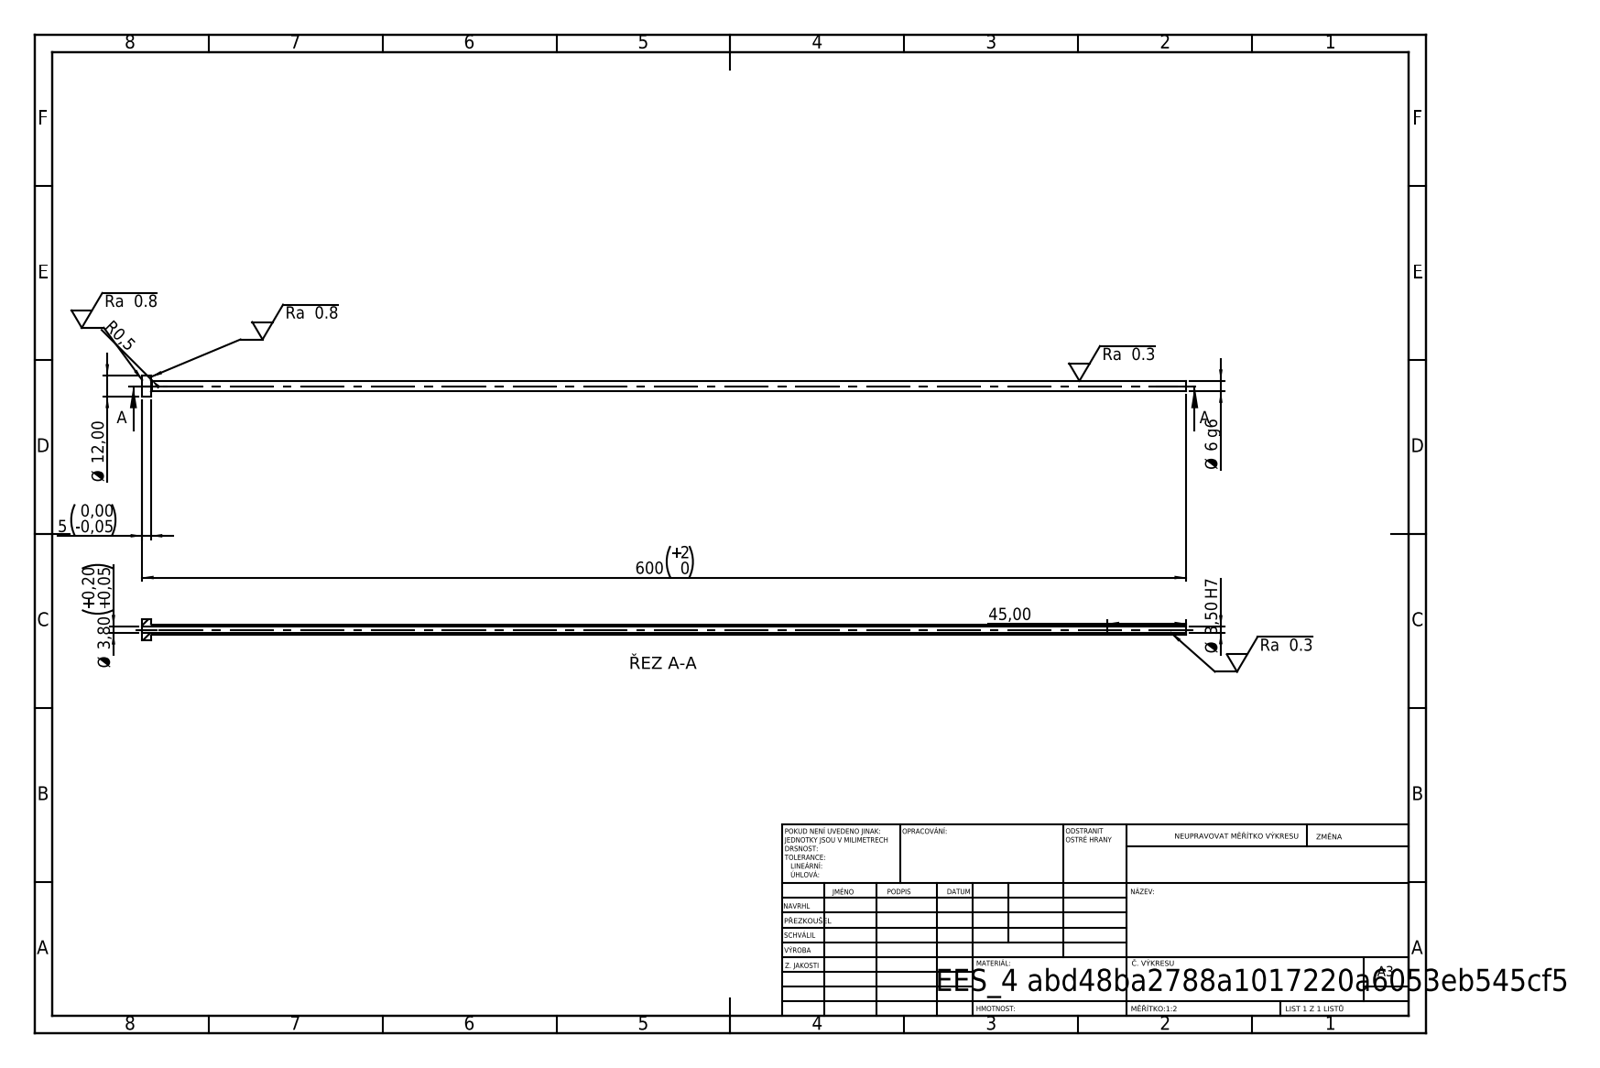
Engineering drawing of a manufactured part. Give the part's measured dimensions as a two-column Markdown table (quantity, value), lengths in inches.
| quantity | value |
| --- | --- |
| STEP written by | SolidWorks 2019 (CONFIG_CONTROL_DESIGN) |
| units | inches |
| bodies | 1 solid, 14 faces (4 planar, 8 cylindrical, 2 other) |
| overall size | 23.622 × 0.472 × 0.472 |
| volume | 0.651 in³ |
| surface area | 29.03 in² |
| round holes (diameter × count) | 0.138 × 1, 0.15 × 1 |
| round bosses / shafts (diameter × count) | 0.472 × 1, 0.236 × 1 |
| main face-to-face distances | 0.197, 23.622, 23.425, 21.85, 21.654, 1.772 |
